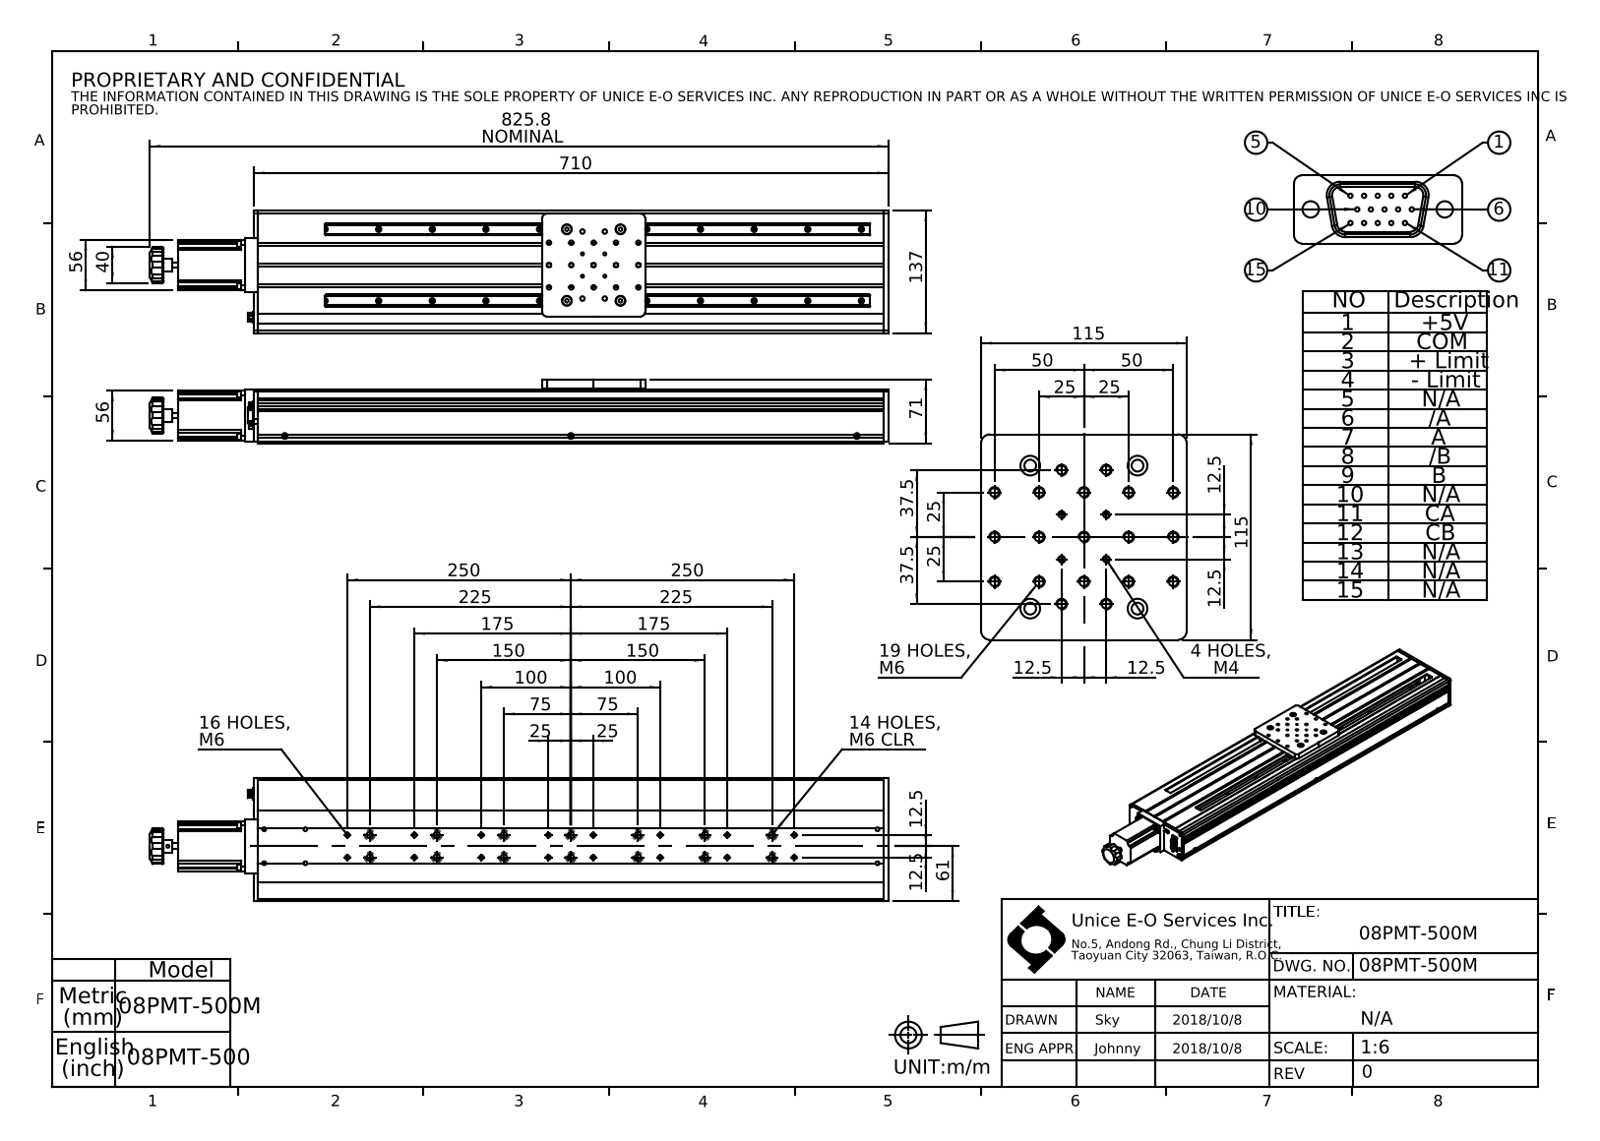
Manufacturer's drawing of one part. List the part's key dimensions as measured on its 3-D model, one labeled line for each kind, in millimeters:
Part name (STEP PRODUCT): 08PMT-500M
STEP written by: SolidWorks 2016 (AUTOMOTIVE_DESIGN)
Units: millimetres
Bodies: 0 solids, 733 faces (324 planar, 306 cylindrical, 103 other)
Overall size (bounding box): 825.8 × 137 × 71
Round holes (diameter × count): ⌀5 ×35, ⌀11 ×18, ⌀7 ×14, ⌀0.8 ×10, ⌀3.3 ×6, ⌀4.2 ×6, ⌀1 ×2, ⌀2 ×2, ⌀2.5 ×2, ⌀18 ×1, ⌀22 ×1, ⌀25.5 ×1
Round bosses / shafts (diameter × count): ⌀6.5 ×4, ⌀5.8 ×3, ⌀7.7 ×2, ⌀3 ×2, ⌀16 ×1, ⌀15 ×1, ⌀6.35 ×1
Partial cylindrical surfaces — rounded edges, fillets, slot ends (radius × count): R1.5 ×9, R4 ×8, R5 ×8, R7.41 ×8, R0.5 ×7, R2 ×4, R4.5 ×4, R3 ×3
Main face-to-face distances: 2, 60.5, 135, 133, 1.5, 10.5, 59, 137, 1.7, 9
Hole centre spacings: 25, 75, 79.06, 150, 152.07, 35.36, 100, 103.08
